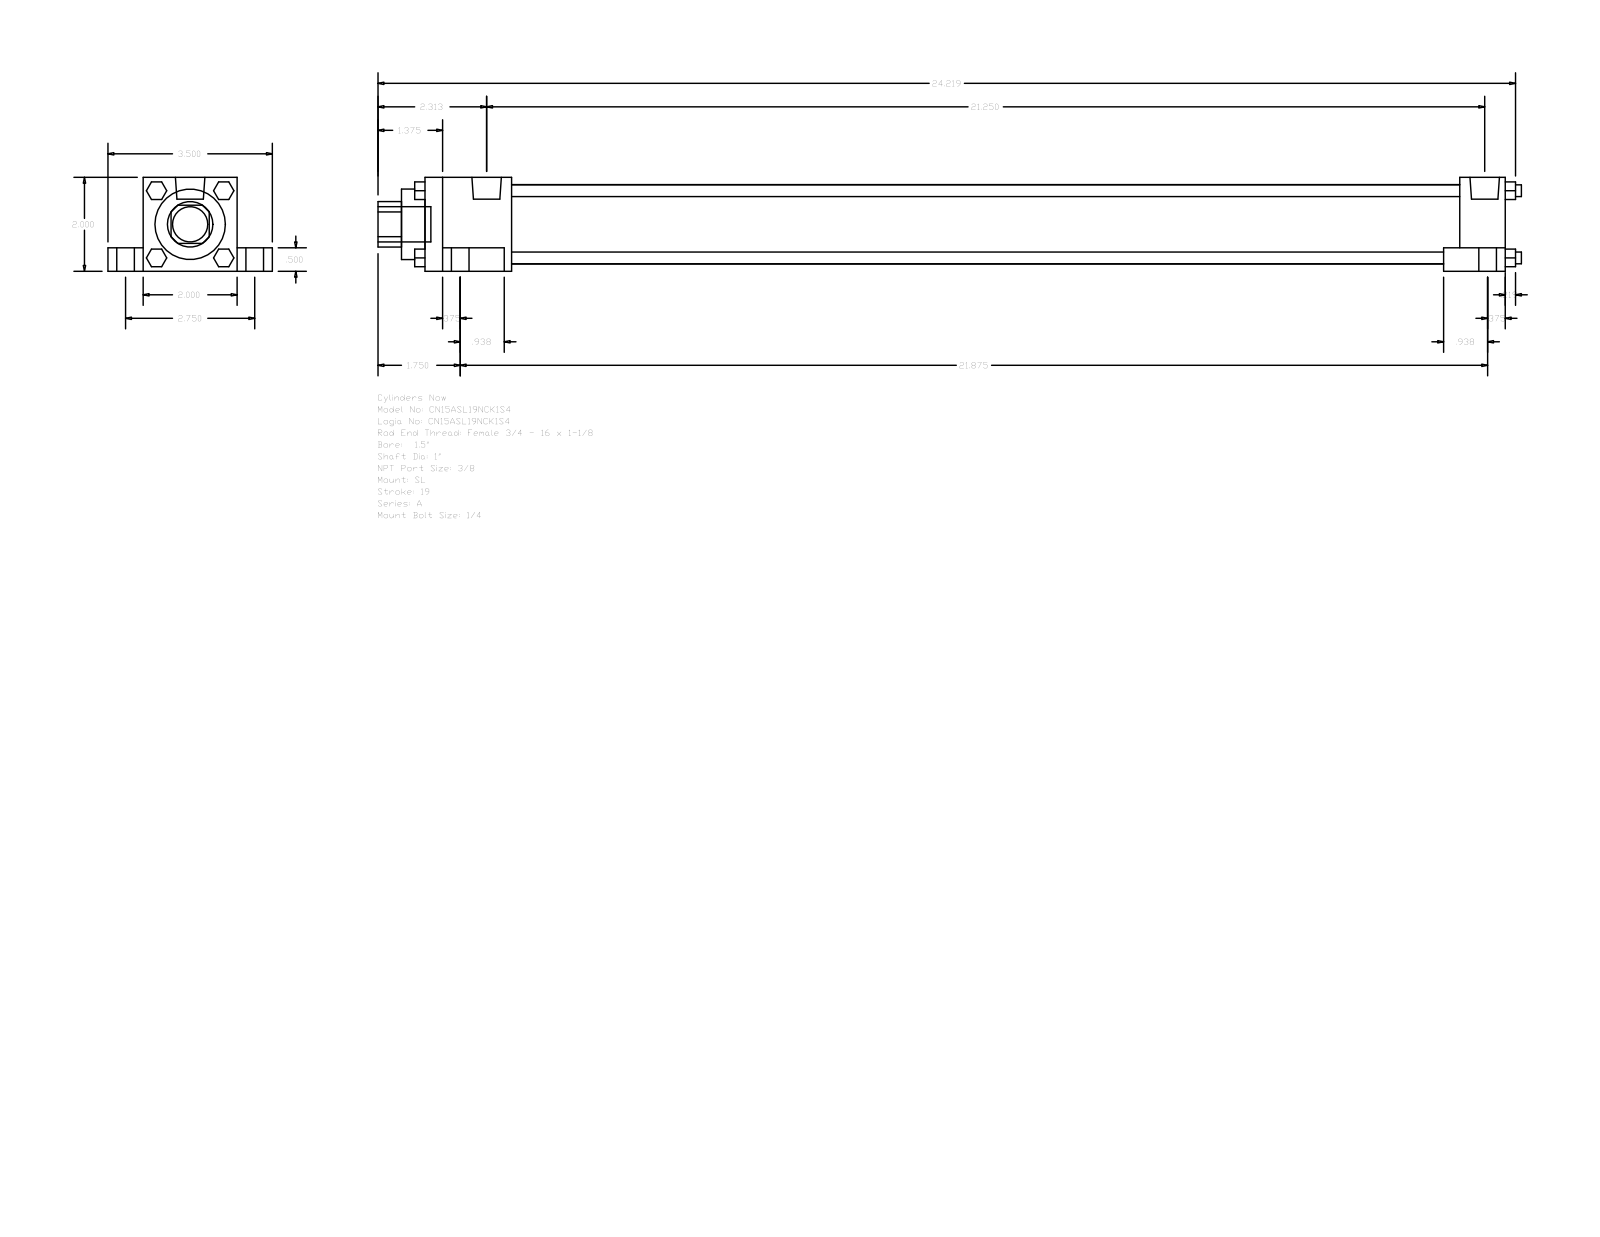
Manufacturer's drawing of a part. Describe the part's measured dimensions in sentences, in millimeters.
The part is named "A_SL__0150_1". Its 3-D file was written by "GSSL Pune (CONFIG_CONTROL_DESIGN)". It is 0 solids with 148 faces: 112 planar, 36 cylindrical and 0 other. Overall it measures 618.33 by 88.9 by 50.8 millimeters. Round holes: 1 of diameter 25.4, 1 of diameter 38.1, 1 of diameter 42.93. Round bosses or shafts: 4 of diameter 15.88, 4 of diameter 9.53, 4 of diameter 6.35, 4 of diameter 5.56, 2 of diameter 15.93, 1 of diameter 19.05. Partial cylindrical surfaces (rounded edges, fillets, slot ends): 1 of radius 12.29. The main face-to-face distances are 50.8, 12.7, 38.1, 19.05, 69.85, 9.52, 584.2, 33.34, 559.59, 24.61.
